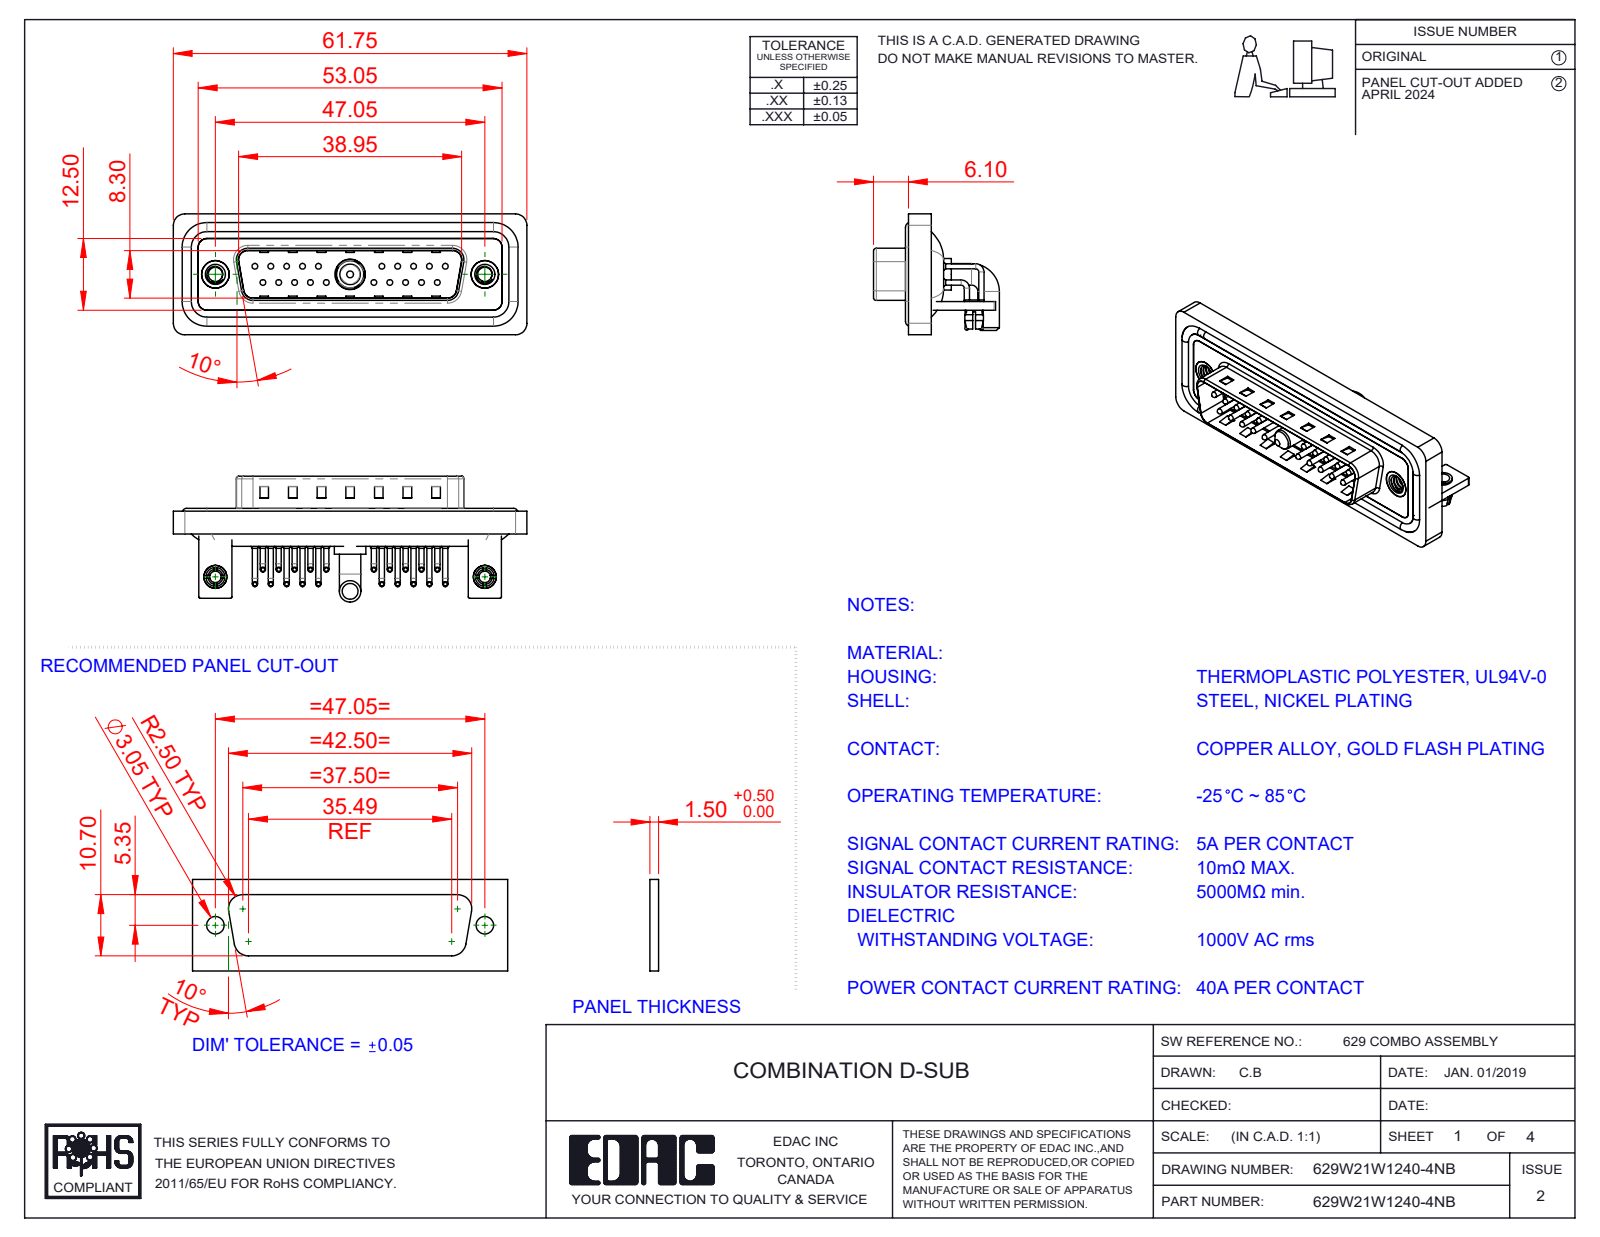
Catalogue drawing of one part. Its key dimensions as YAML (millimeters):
part_name: "629Combo Housing_21W1; 629Combo Stabilizer Bracket; Power Pin_40A RA; 629Combo Shell Front_25 Contacts (+7 more)"
step_written_by: "SolidWorks 2023 (CONFIG_CONTROL_DESIGN)"
units: millimeters
bodies: {solids: 33, faces: 2856, planar: 1567, cylindrical: 979, other: 310}
overall_size: [61.75, 21.98, 21.1]
volume: 7799
surface_area: 13563
round_holes:
  - {diameter: 2, count: 22}
  - {diameter: 0.75, count: 20}
  - {diameter: 1.6, count: 20}
  - {diameter: 2.5, count: 4}
  - {diameter: 3.2, count: 2}
  - {diameter: 4, count: 2}
  - {diameter: 4.8, count: 2}
  - {diameter: 5, count: 2}
  - {diameter: 4.85, count: 1}
  - {diameter: 5.3, count: 1}
round_bosses_or_shafts:
  - {diameter: 0.9, count: 40}
  - {diameter: 1.5, count: 20}
  - {diameter: 1, count: 20}
  - {diameter: 0.65, count: 20}
  - {diameter: 1.6, count: 4}
  - {diameter: 4.9, count: 2}
  - {diameter: 4, count: 2}
  - {diameter: 3.75, count: 2}
partial_cylinders:
  - {radius: 1.01, count: 20}
  - {radius: 2, count: 19}
  - {radius: 1.5, count: 18}
  - {radius: 0.25, count: 16}
  - {radius: 0.5, count: 9}
  - {radius: 1.6, count: 8}
  - {radius: 0.6, count: 4}
  - {radius: 0.65, count: 4}
face_to_face_distances: [0.4, 0.8, 2.1, 2.9, 1.5, 1.1, 4.1, 1.6, 4.5, 3.7]
hole_center_spacings: [3.16, 2.77, 5.54, 8.31, 5.04, 19.39, 20.97, 22.16]
